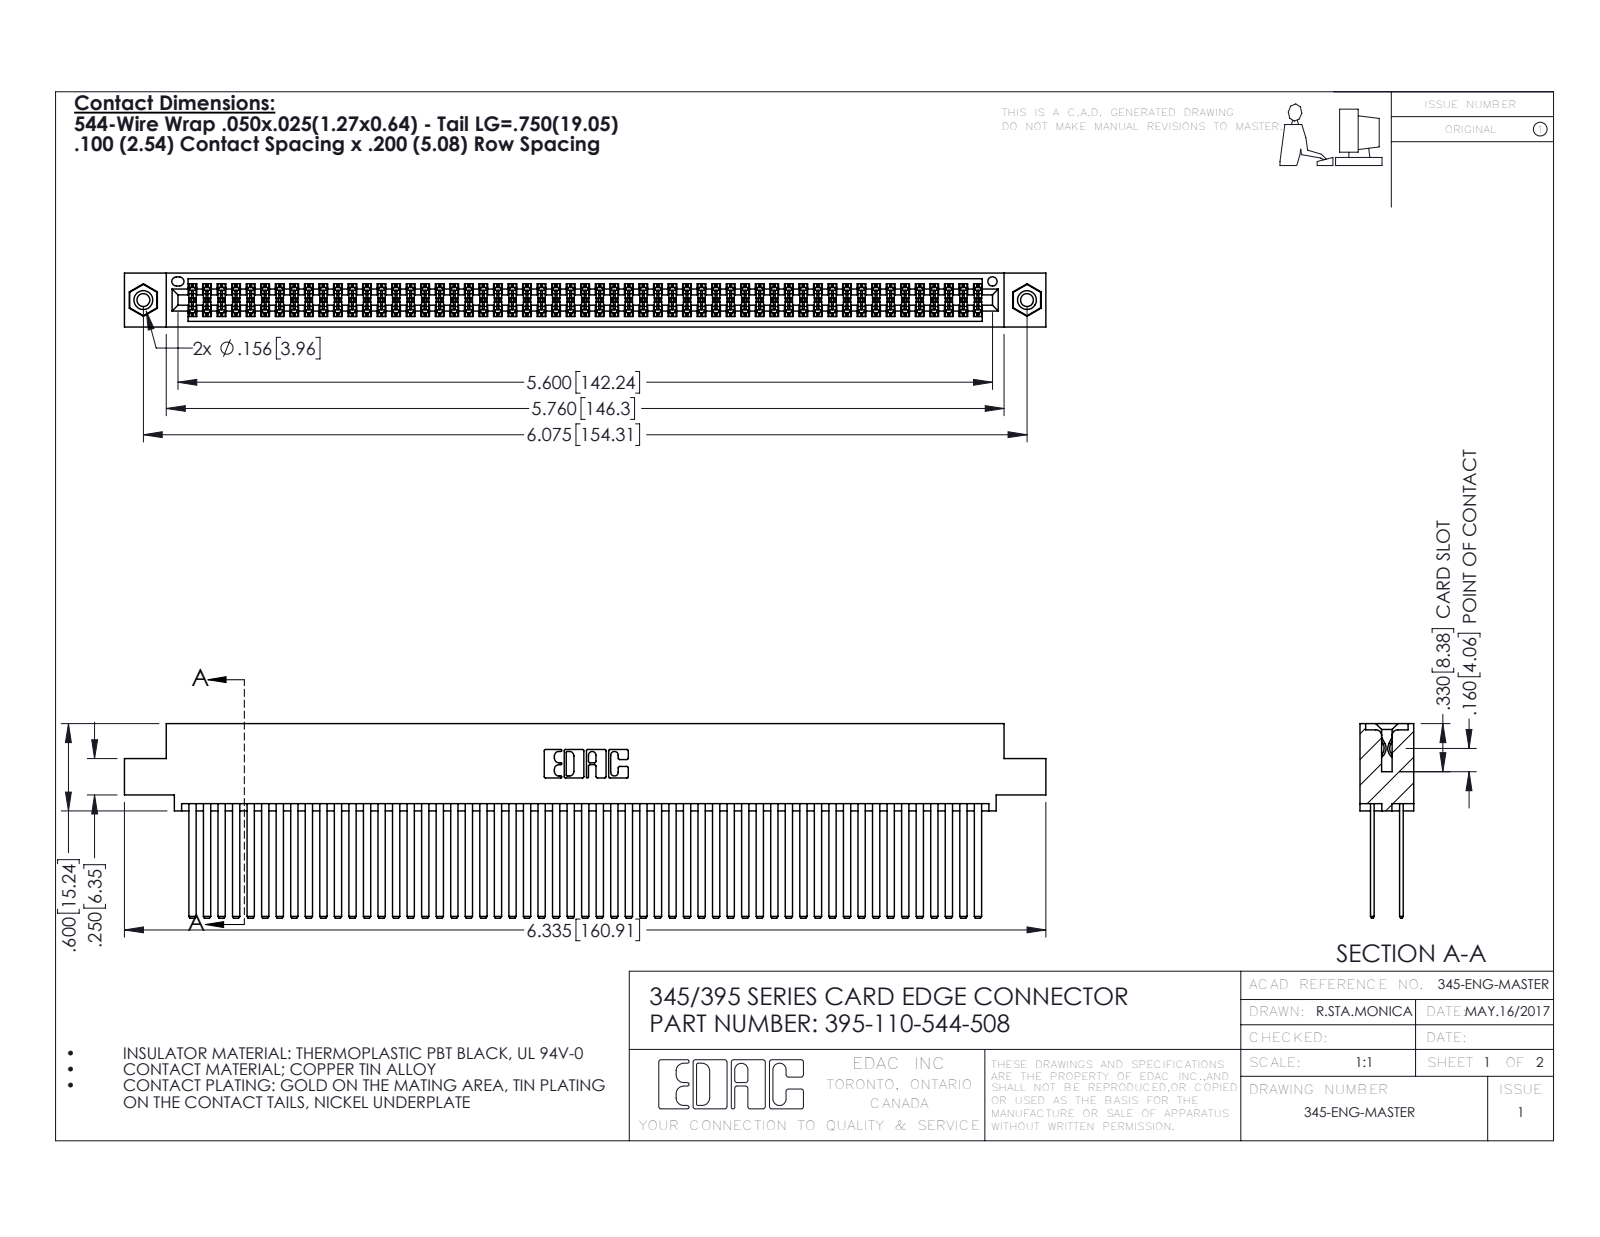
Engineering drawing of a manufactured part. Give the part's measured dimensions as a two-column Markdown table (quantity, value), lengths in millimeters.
| quantity | value |
| --- | --- |
| part name | 345-250-001_345-250-003-102; 395-110-544-508; 345 Part_0.110 Offset - 0.156 Dia-TI; 345-292-001_345-293-144 |
| STEP written by | SolidWorks 2016 (CONFIG_CONTROL_DESIGN) |
| units | millimeters |
| bodies | 113 solids, 5030 faces (3306 planar, 1708 cylindrical, 16 other) |
| overall size | 160.9 × 34 × 9.4 |
| volume | 17 210 mm³ |
| surface area | 30 320 mm² |
| round holes (diameter × count) | 2.3 × 2, 3.2 × 2, 4 × 2, 1.6 × 1 |
| round bosses / shafts (diameter × count) | 3.9 × 2 |
| partial cylindrical surfaces (radius × count) | 0.2 × 165, 0.3 × 22, 0.2 × 6, 0.8 × 6, 0.7 × 3, 0.4 × 2, 0.5 × 2, 0.6 × 2 |
| main face-to-face distances | 5.1, 0.6, 1.8, 2.5, 6.9, 7.6, 5.7, 4.4, 9.4, 1.3 |
| hole center spacings | 6.9, 148.3, 154.3 |
